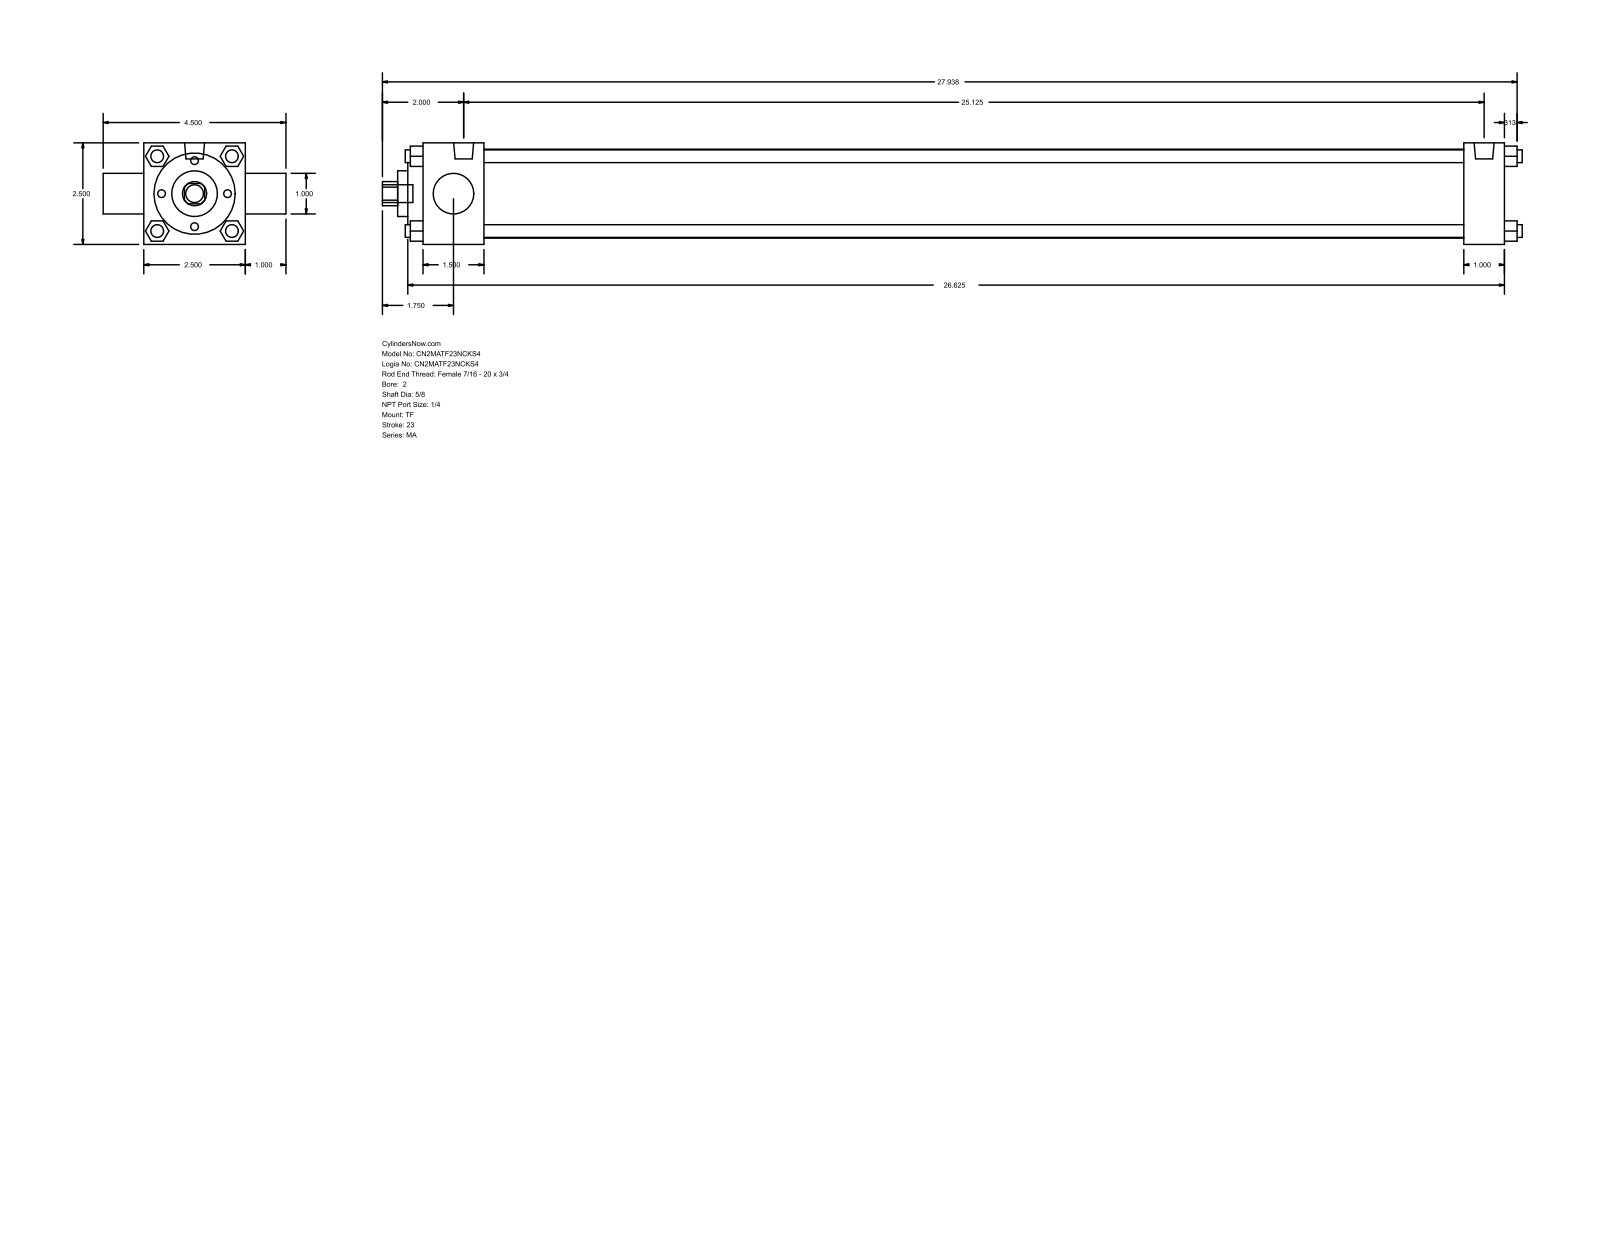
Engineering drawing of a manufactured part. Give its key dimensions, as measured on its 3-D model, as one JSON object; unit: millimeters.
{"part_name": "MA_TF__0200_0.625", "step_written_by": "GSSL Pune (CONFIG_CONTROL_DESIGN)", "units": "millimeters", "bodies": {"solids": 0, "faces": 122, "planar": 93, "cylindrical": 29, "other": 0}, "overall_size": [712.79, 114.3, 63.5], "round_holes": [[15.88, 1], [25.4, 1], [28.57, 1], [50.8, 1], [55.63, 1]], "round_bosses_or_shafts": [[7.94, 7], [12.49, 2], [11.11, 1]], "partial_cylinders_radius": [[7.54, 1]], "face_to_face_distances": [63.5, 25.4, 38.1, 12.7, 676.27, 9.52, 650.87, 612.77, 638.17, 47.62]}
